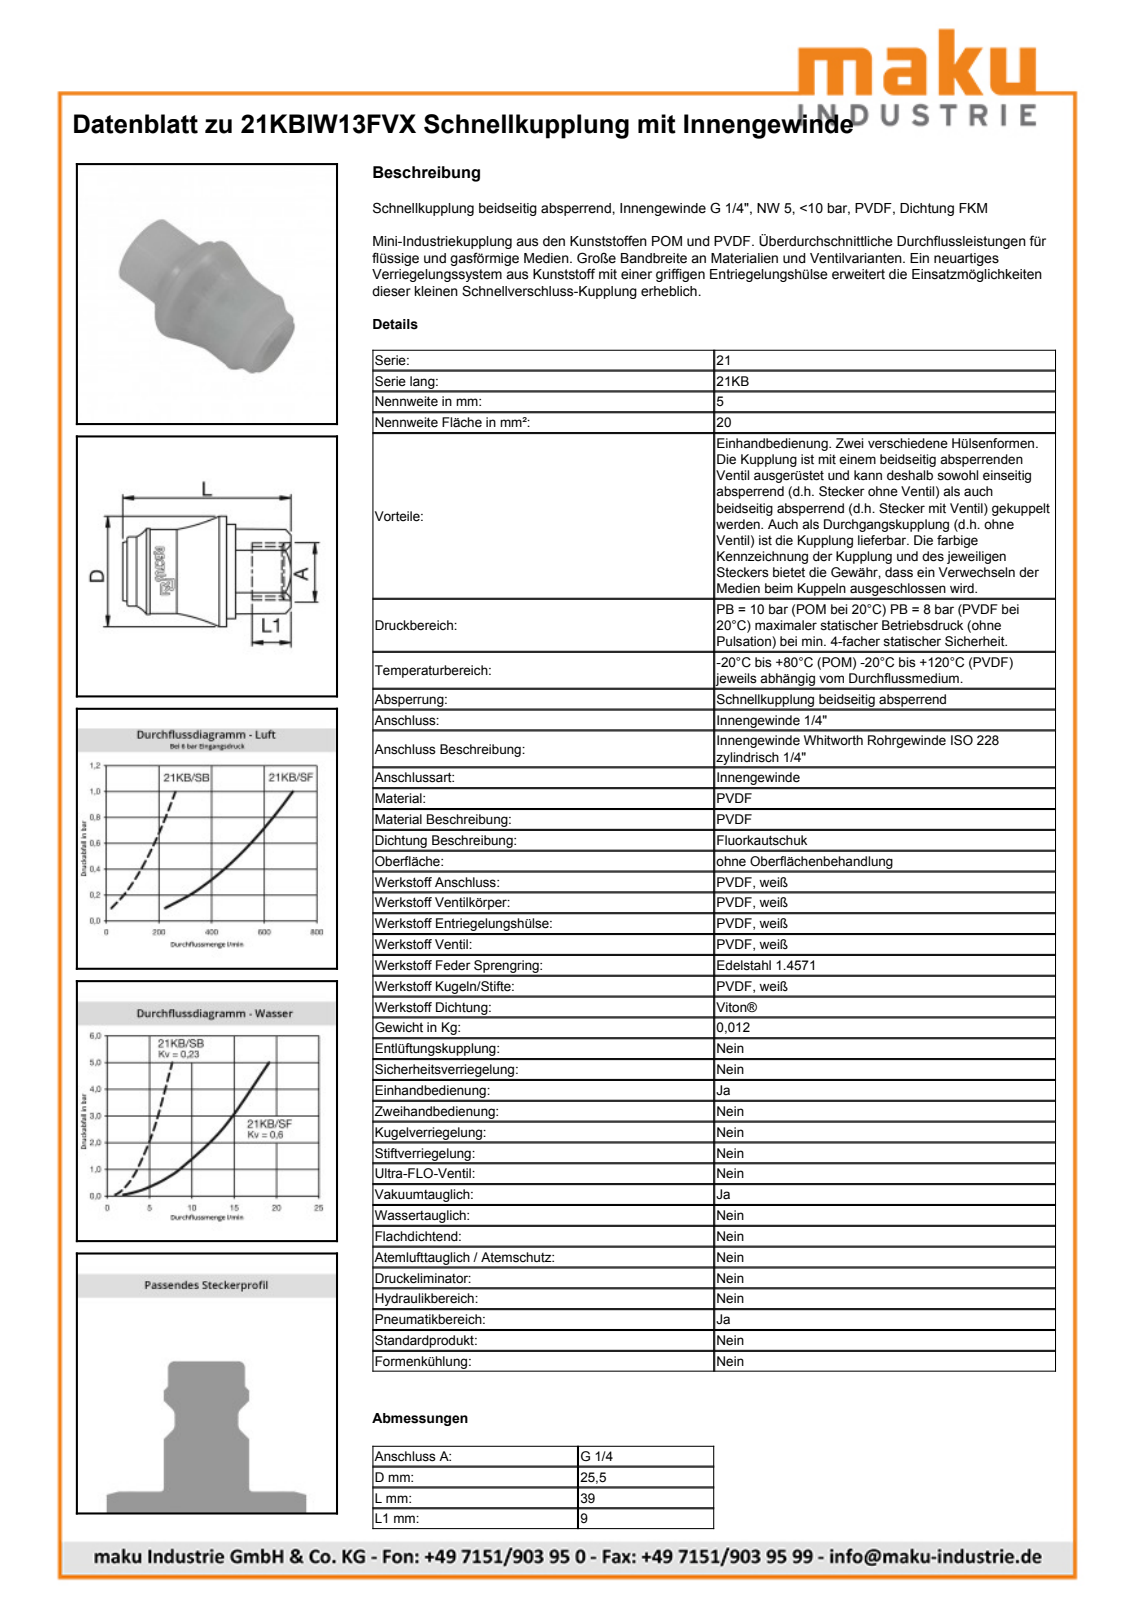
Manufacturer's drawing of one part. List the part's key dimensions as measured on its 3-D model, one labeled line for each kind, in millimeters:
Part name (STEP PRODUCT): D111910
STEP written by: Autodesk Inventor 2013 (AUTOMOTIVE_DESIGN)
Units: millimetres
Bodies: 1 solid, 210 faces (127 planar, 31 cylindrical, 52 other)
Overall size (bounding box): 38.8 × 25.3 × 25.3
Volume: 8 324 mm³ · Surface area: 6 151 mm²
Round holes (diameter × count): ⌀11.02 ×1, ⌀13.15 ×1, ⌀13.5 ×1, ⌀16.3 ×1, ⌀22 ×1
Round bosses / shafts (diameter × count): ⌀25.3 ×1, ⌀21.9 ×1, ⌀19.65 ×1, ⌀19.3 ×1, ⌀15.8 ×1, ⌀14.15 ×1, ⌀13.35 ×1, ⌀13.02 ×1
Partial cylindrical surfaces — rounded edges, fillets, slot ends (radius × count): R9.85 ×1
Main face-to-face distances: 16.8, 26, 2.9, 28.9, 5.05, 9.9, 12.8, 38.8, 14.95, 2.15
